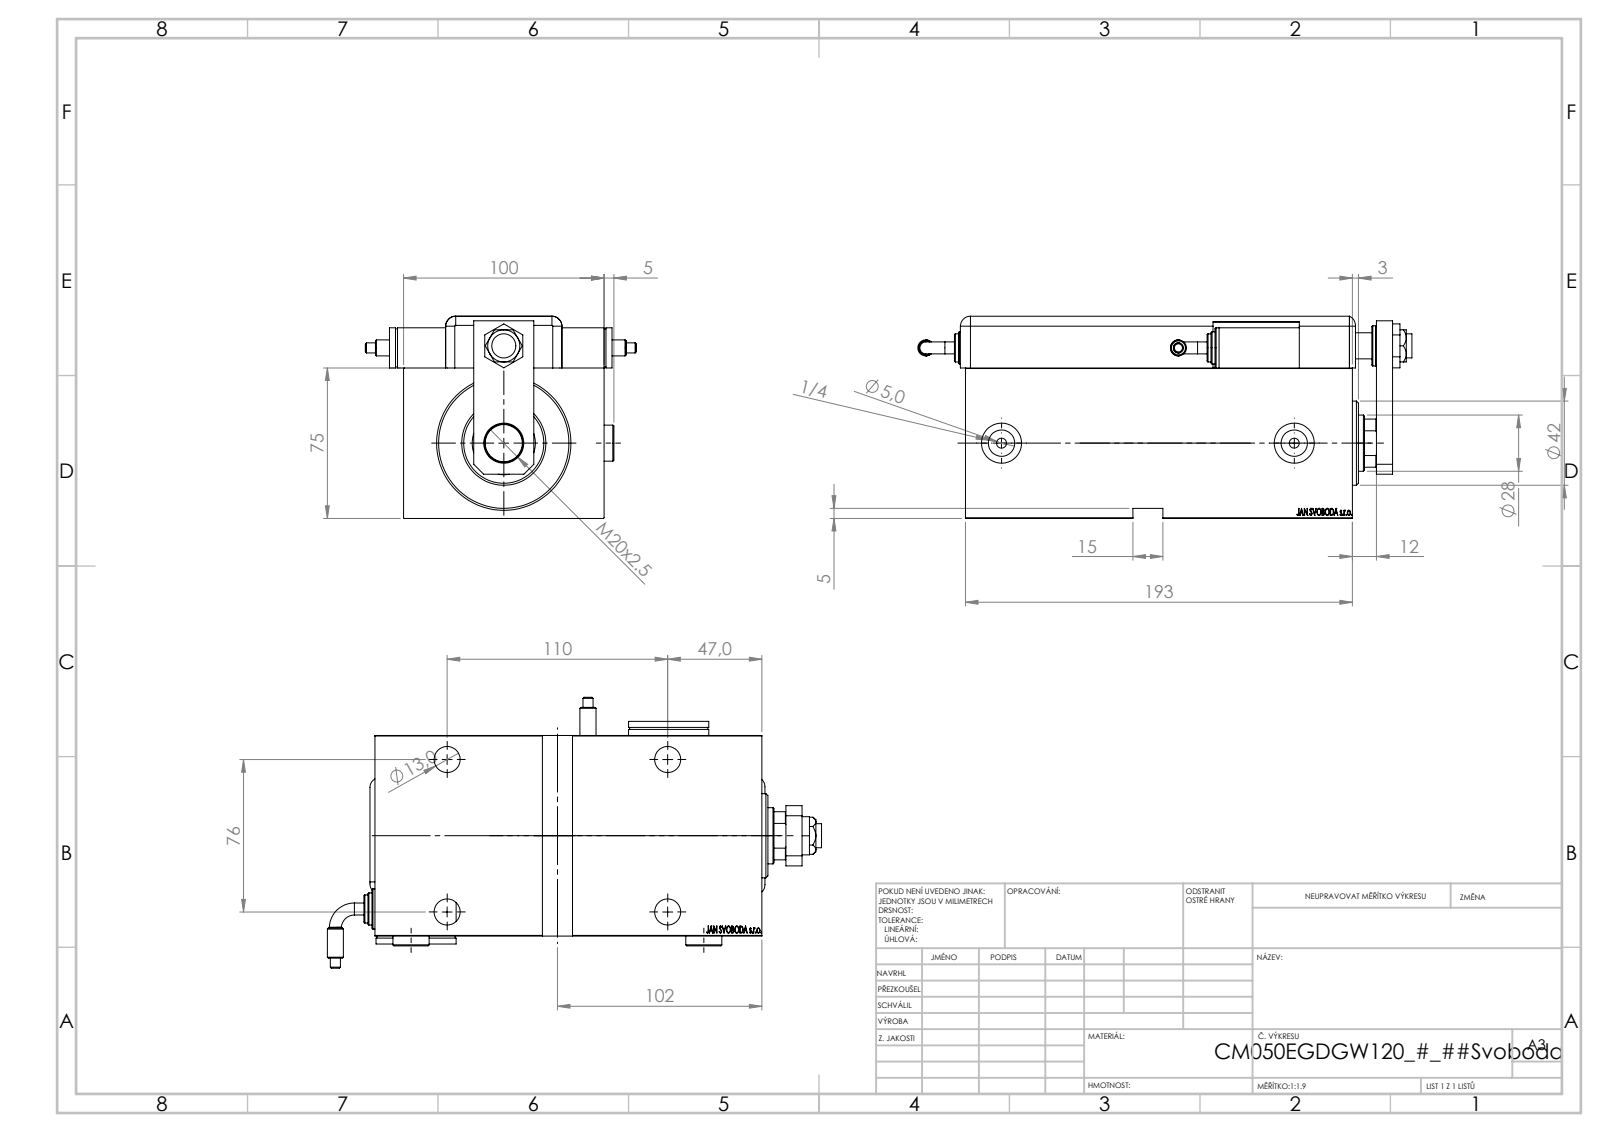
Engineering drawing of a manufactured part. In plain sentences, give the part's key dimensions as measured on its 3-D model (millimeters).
The part is named "NUT_D19; SWITCH DIM A_G; NUT_D13; V450CM_E_Body (+7 more)". Its 3-D file was written by "SolidWorks 2019 (CONFIG_CONTROL_DESIGN)". It is 15 solids with 1324 faces: 656 planar, 131 cylindrical and 537 other. Overall it measures 246.46 by 135.01 by 100.8 millimeters. Its volume is 1 416 000 cubic millimeters and its surface area 243 472 square millimeters. Round holes: 5 of diameter 13, 4 of diameter 19, 3 of diameter 20, 2 of diameter 4, 2 of diameter 5, 2 of diameter 8, 2 of diameter 13.16, 1 of diameter 12, 1 of diameter 14, 1 of diameter 18.5, 1 of diameter 28, 1 of diameter 31.5. Round bosses or shafts: 3 of diameter 20, 2 of diameter 18, 2 of diameter 16, 2 of diameter 14, 2 of diameter 8, 2 of diameter 6, 2 of diameter 5.04, 1 of diameter 52. Partial cylindrical surfaces (rounded edges, fillets, slot ends): 9 of radius 5, 1 of radius 10, 1 of radius 13.5. The main face-to-face distances are 75, 3, 100, 100.8, 25.8, 22.8, 97.8, 21, 79, 193. The hole center spacings are 47.2, 61.22, 76, 110, 133.7, 150.63, 155.59, 20.
